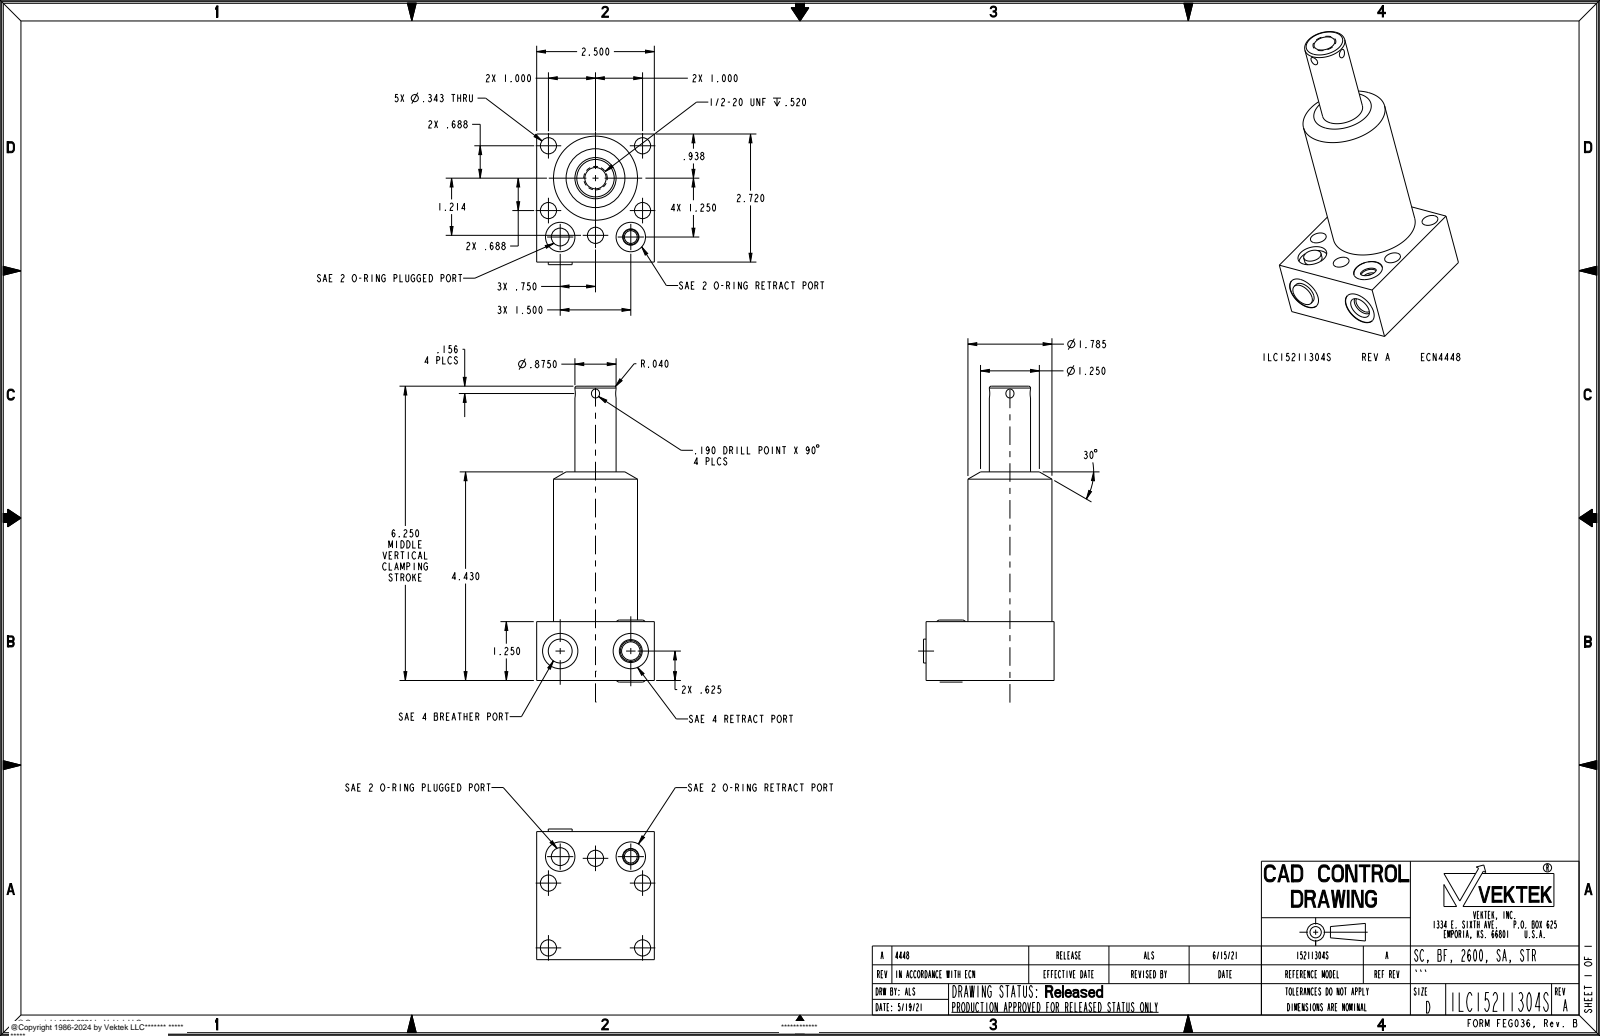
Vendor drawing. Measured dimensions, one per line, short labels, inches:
name: ILC15211304S
written by: PRO/ENGINEER BY PARAMETRIC TECHNOLOGY CORPORATION, 2013320 (CONFIG_CONTROL_DESIGN)
unit: in
bodies: 3 solids, 105 faces (21 planar, 46 cylindrical, 38 other)
size: 6.284 × 2.775 × 2.5
volume: 16.5 in³; area: 61.57 in²
holes: 5× ⌀0.343, 2× ⌀0.392, 2× ⌀0.625, 2× ⌀0.75, 1× ⌀0.272, 1× ⌀0.453
bosses: 1× ⌀1.785, 1× ⌀0.875, 1× ⌀0.507, 1× ⌀0.5, 1× ⌀0.378
face distances: 2.5, 1.25, 2.72, 0.105, 1.145, 2.71, 4.43, 3.18, 1.04, 4.325
hole spacings: 1.214, 0.615, 0.751, 1.13, 1.376, 1.458, 1.5, 1.838
